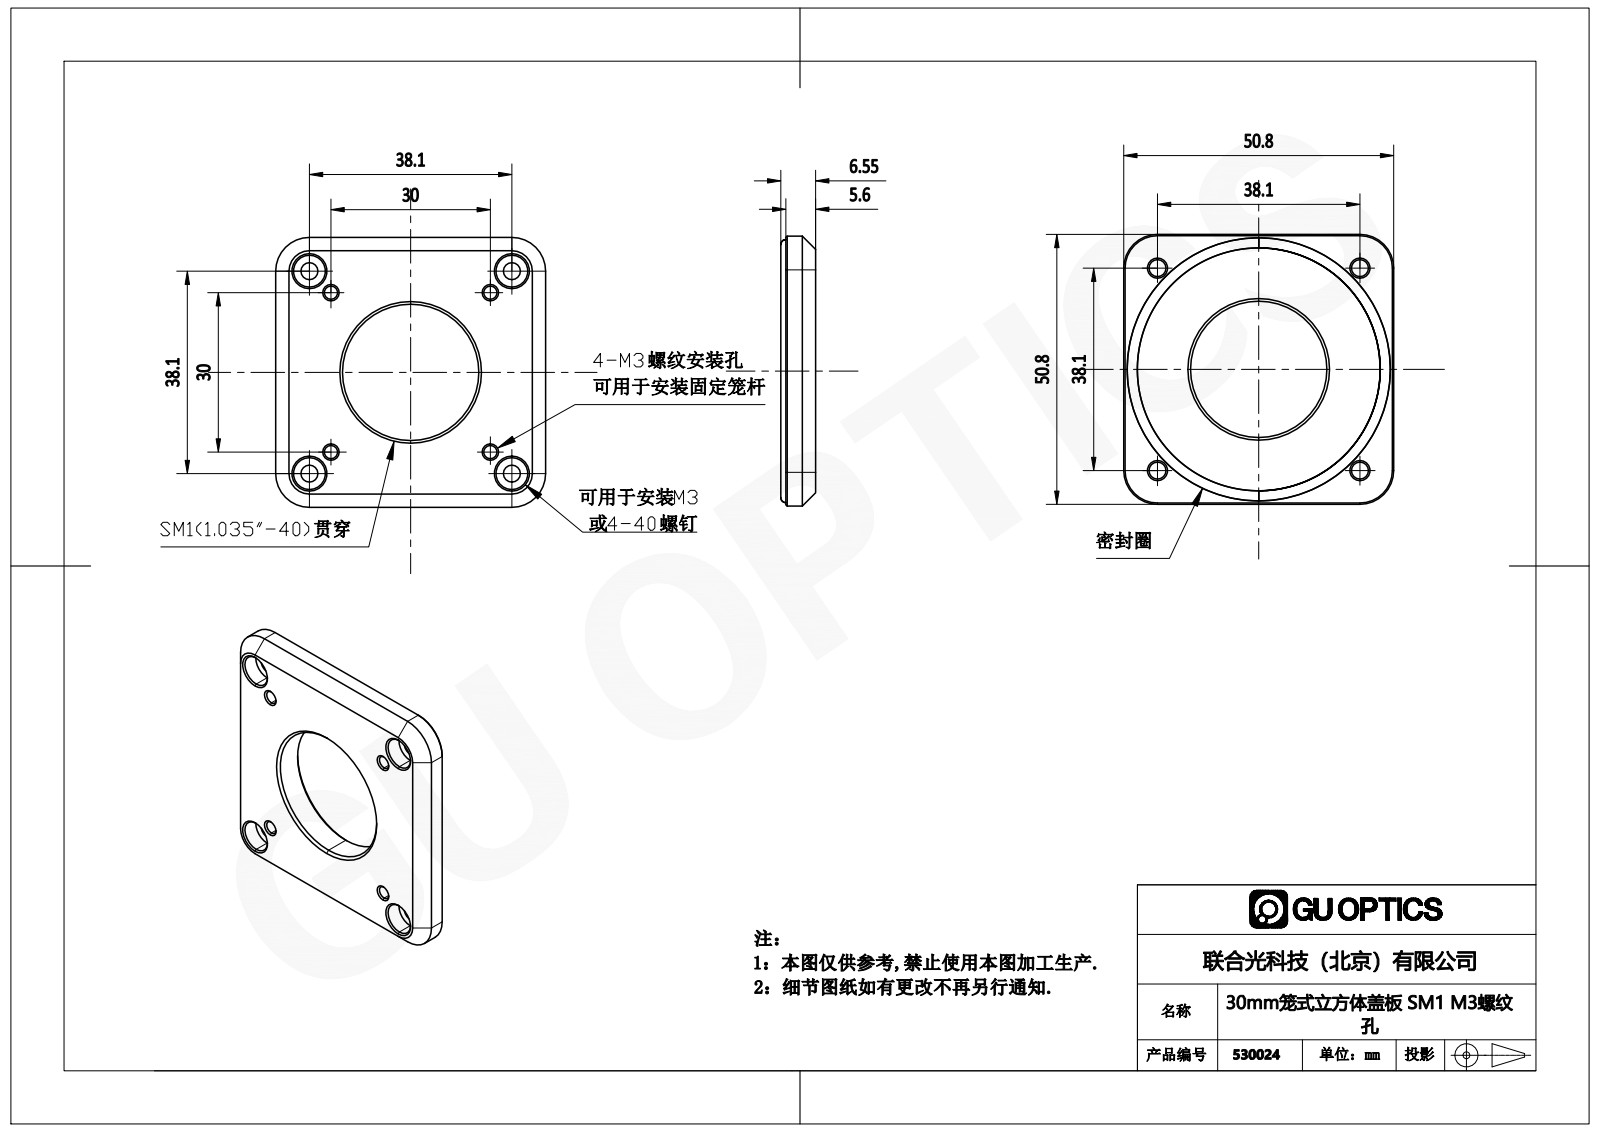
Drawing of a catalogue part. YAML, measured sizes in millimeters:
part_name: "2.2.7.29_L30F-GSM1M_30 mm笼式立方体空白板盖板，带SM1螺纹，带M3螺纹孔"
step_written_by: "SolidWorks 2018 (AUTOMOTIVE_DESIGN)"
units: millimeters
bodies: {solids: 0, faces: 94, planar: 20, cylindrical: 34, other: 40}
overall_size: [50.8, 50.8, 6.55]
round_holes:
  - {diameter: 2.5, count: 4}
  - {diameter: 3.2, count: 4}
  - {diameter: 6, count: 4}
  - {diameter: 25.65, count: 1}
  - {diameter: 49.53, count: 1}
round_bosses_or_shafts:
  - {diameter: 45.72, count: 1}
partial_cylinders:
  - {radius: 6.35, count: 4}
face_to_face_distances: [5.6, 4.08, 1.52, 50.8, 3.2, 0.88, 2.4, 37.93]
hole_center_spacings: [34.29, 5.73, 21.21, 26.94, 30, 38.1, 48.15, 42.43]
